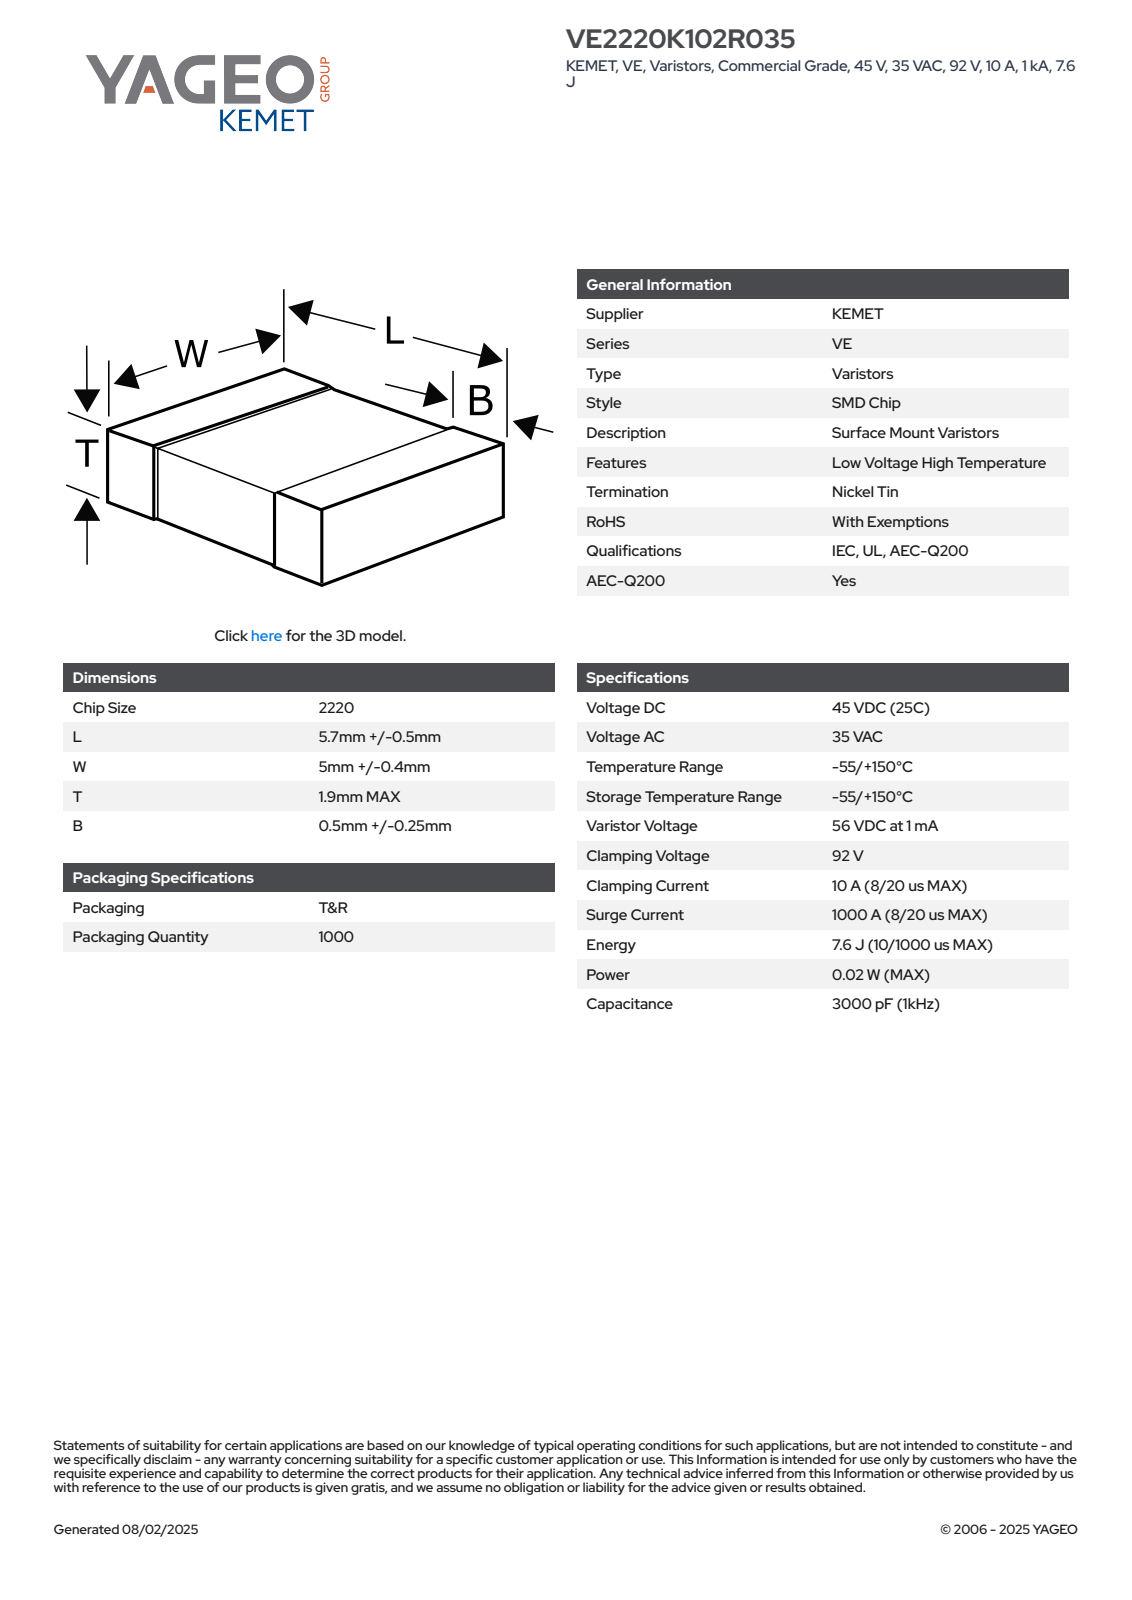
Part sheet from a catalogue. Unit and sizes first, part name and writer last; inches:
Units: inches
Overall size (bounding box): 0.244 × 0.213 × 0.075
Partial cylindrical surfaces — rounded edges, fillets, slot ends (radius × count): R0.004 ×24
Main face-to-face distances: 0.066, 0.07, 0.244, 0.204, 0.075, 0.208, 0.213, 0.112, 0.132, 0.031
Volume: 0.003 in³ · Surface area: 0.171 in²
Bodies: 4 solids, 125 faces (71 planar, 38 cylindrical, 16 other)
Part name (STEP PRODUCT): VS_SMD_2220_L6.2W5.4T1.9B0.75
STEP written by: SolidWorks 2021 (AUTOMOTIVE_DESIGN)
